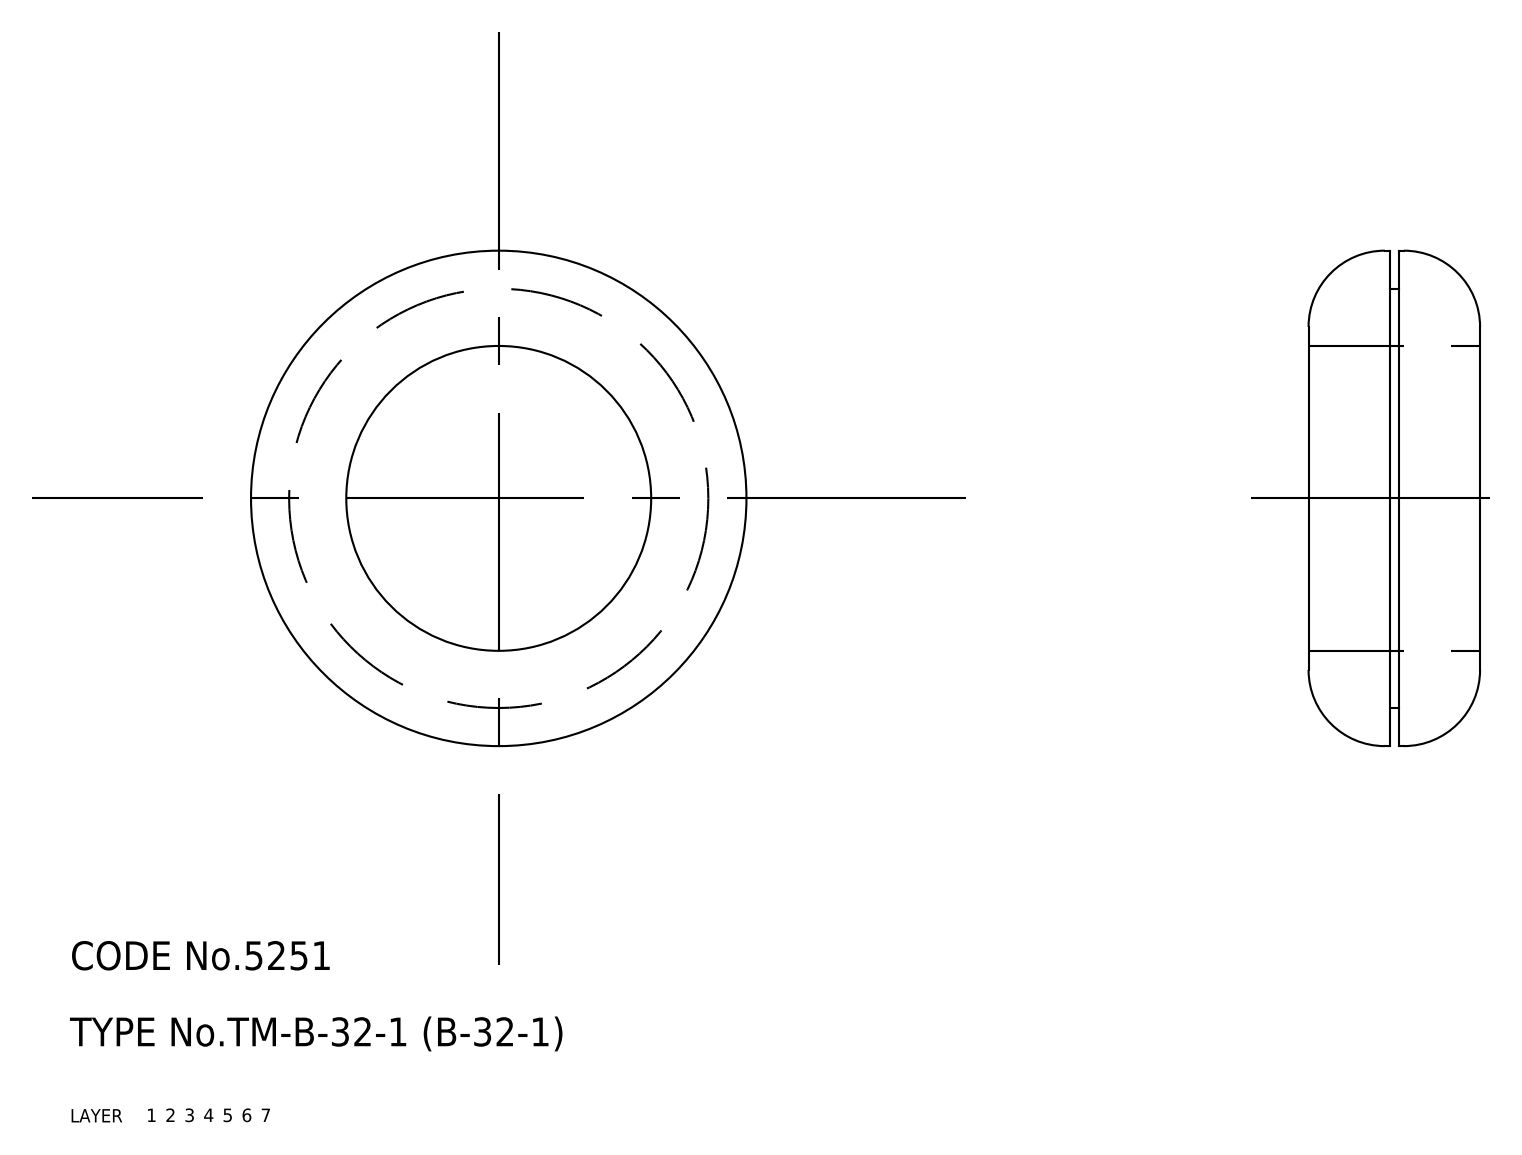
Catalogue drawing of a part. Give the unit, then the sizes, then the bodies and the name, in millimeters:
Units: millimetres
Overall size (bounding box): 52 × 52 × 18
Volume: 19 020 mm³ · Surface area: 7 396 mm²
Bodies: 1 solid, 16 faces (0 planar, 0 cylindrical, 16 other)
Part name (STEP PRODUCT): grommet
STEP written by: CADfix (AUTOMOTIVE_DESIGN)
